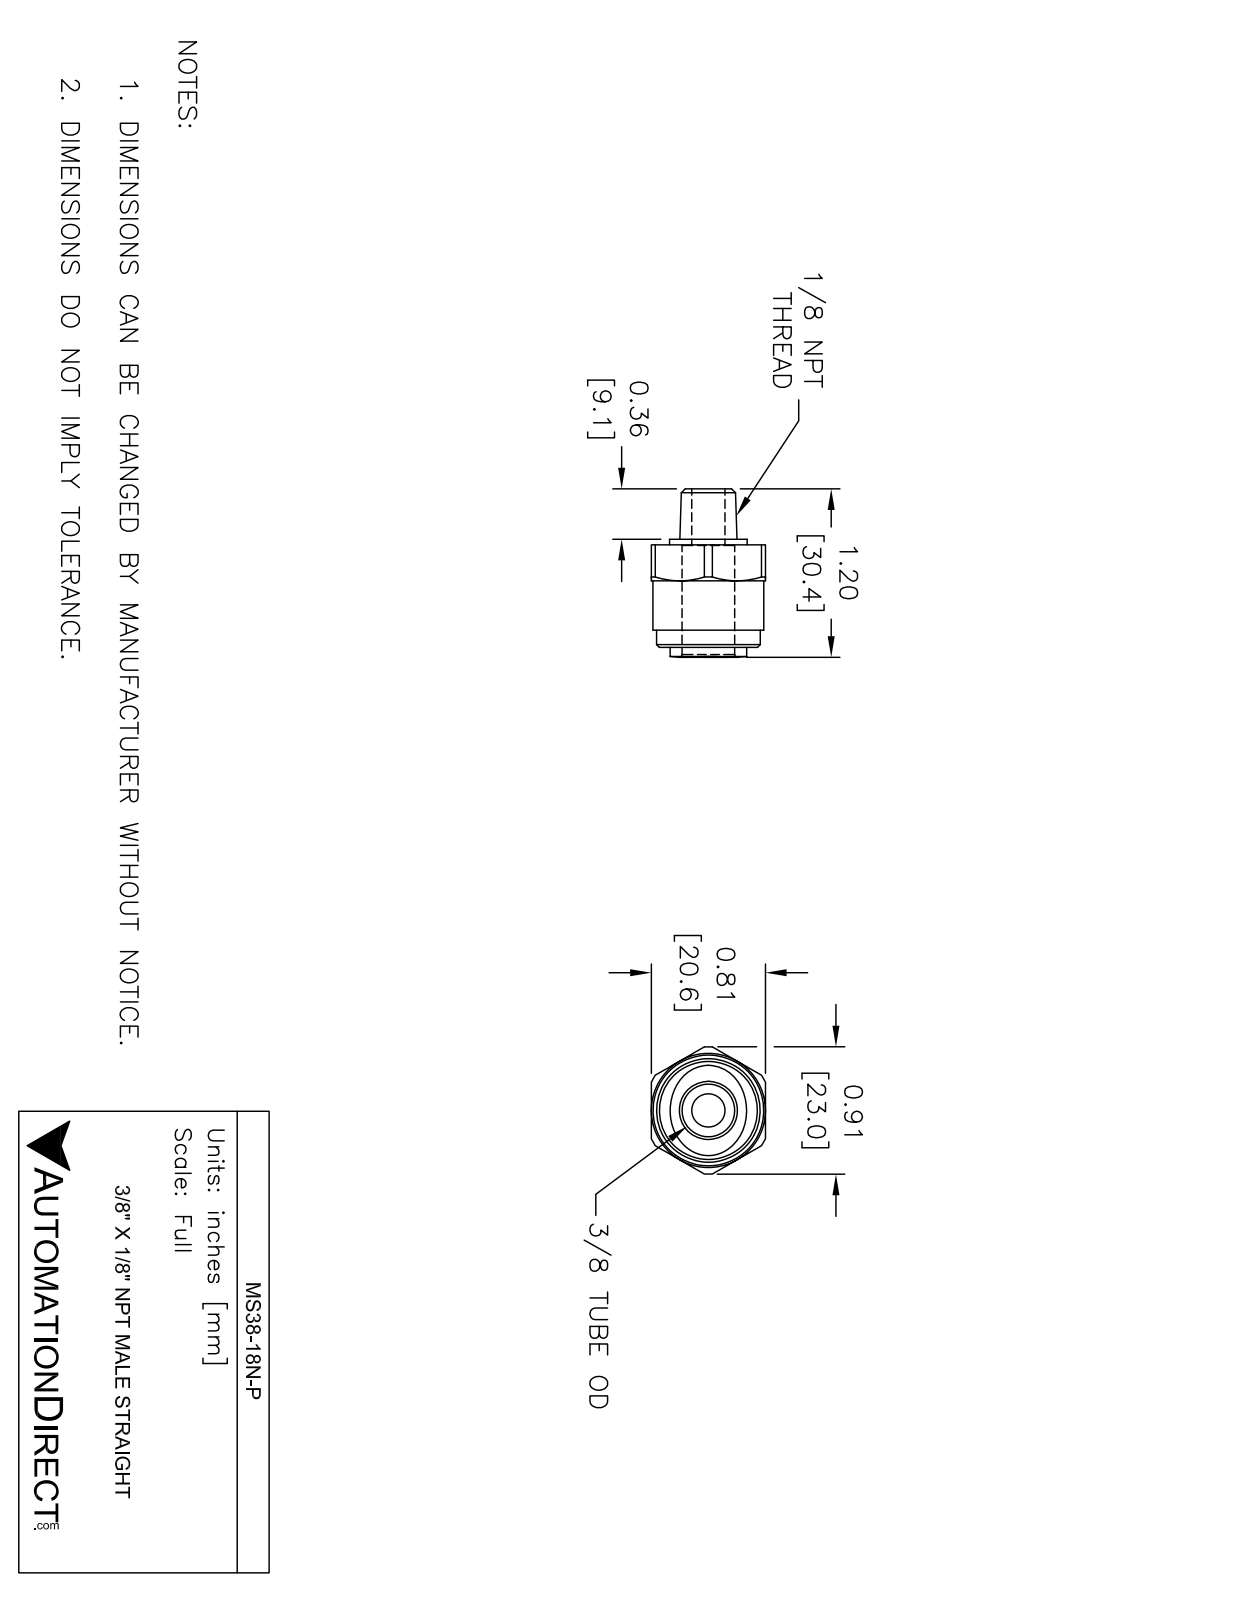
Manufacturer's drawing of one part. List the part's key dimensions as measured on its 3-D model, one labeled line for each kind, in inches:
Part name (STEP PRODUCT): MS38-18N-P
STEP written by: SolidWorks 2017 (AUTOMOTIVE_DESIGN)
Units: inches
Bodies: 1 solid, 49 faces (13 planar, 17 cylindrical, 19 other)
Overall size (bounding box): 1.197 × 0.906 × 0.811
Volume: 0.333 in³ · Surface area: 4.672 in²
Round holes (diameter × count): ⌀0.236 ×1, ⌀0.374 ×1
Round bosses / shafts (diameter × count): ⌀0.787 ×1, ⌀0.736 ×1, ⌀0.551 ×1
Partial cylindrical surfaces — rounded edges, fillets, slot ends (radius × count): R0.453 ×1
Main face-to-face distances: 0.811, 0.039, 0.768, 0.728, 0.043, 0.724, 0.646, 0.606, 0.602, 0.122
